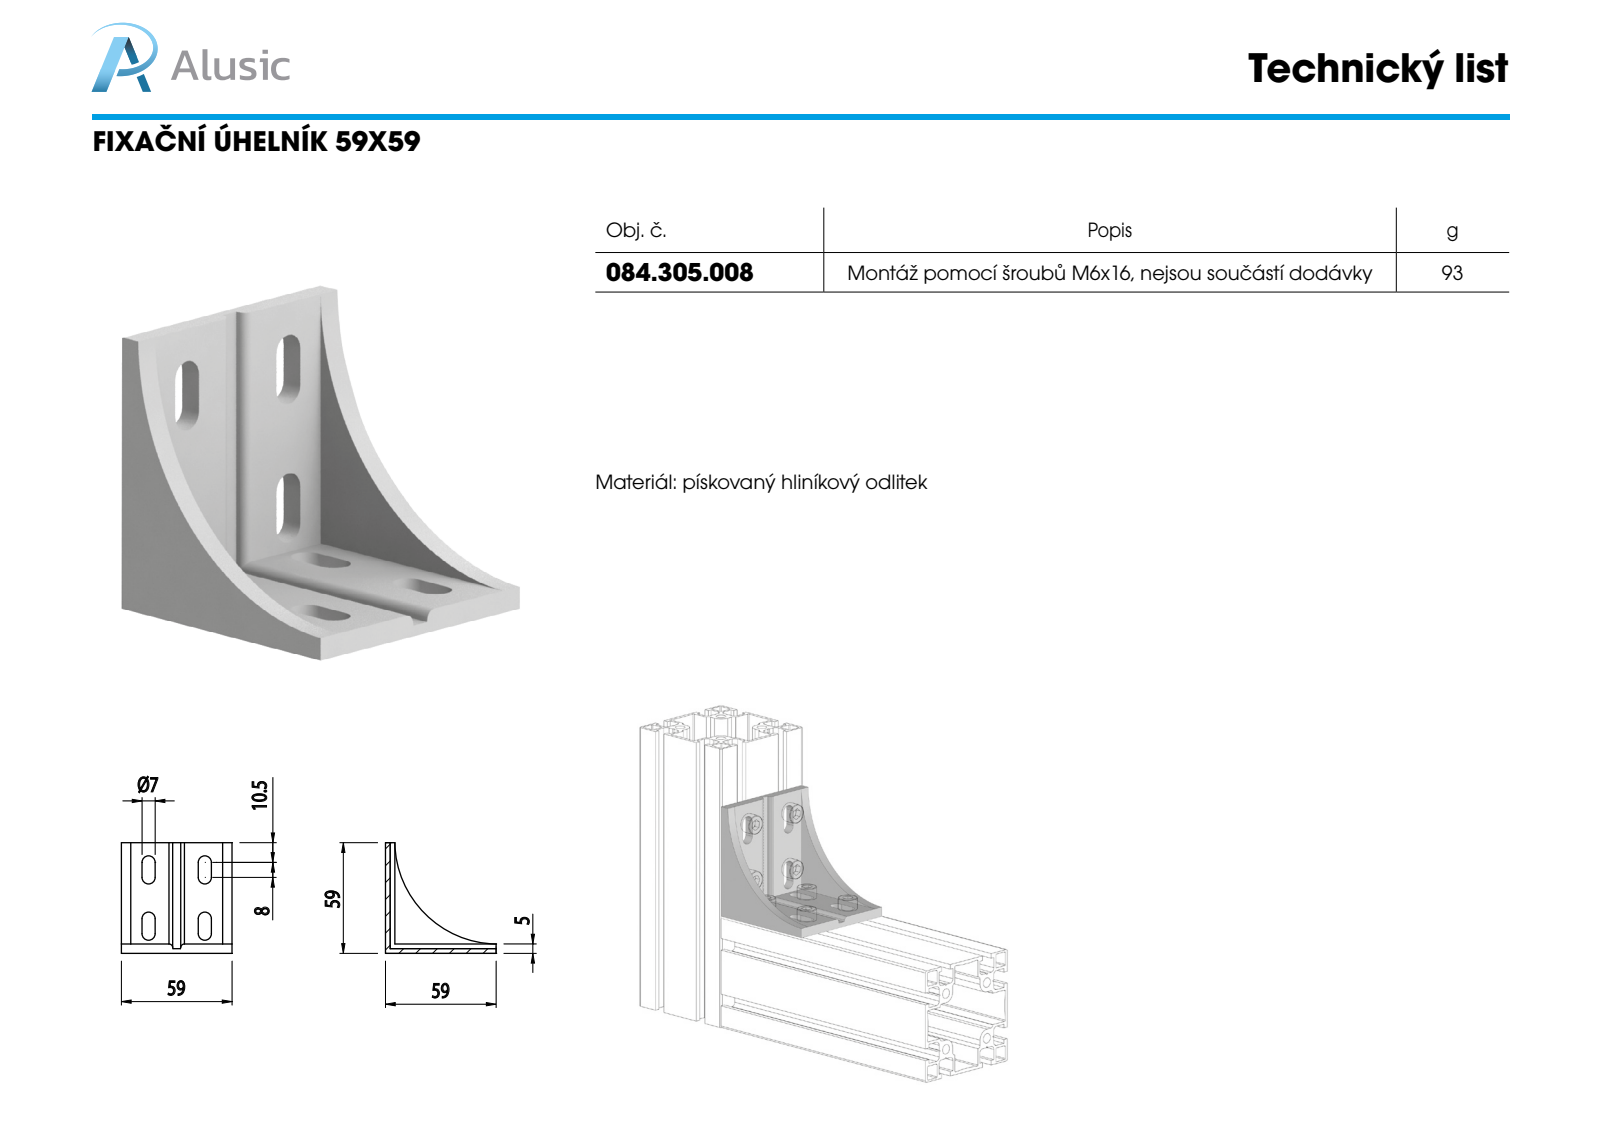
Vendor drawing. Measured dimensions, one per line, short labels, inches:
name: 084.305.008
written by: SolidWorks 2011 (CONFIG_CONTROL_DESIGN)
unit: in
bodies: 1 solid, 62 faces (36 planar, 26 cylindrical, 0 other)
size: 2.323 × 2.323 × 2.323
volume: 2.114 in³; area: 27.14 in²
rounds: 16× R0.144, 8× R0.039, 1× R2.126
face distances: 0.197, 2.323, 0.217, 2.106, 1.89, 2.126, 0.079, 0.118, 2.205, 0.715
